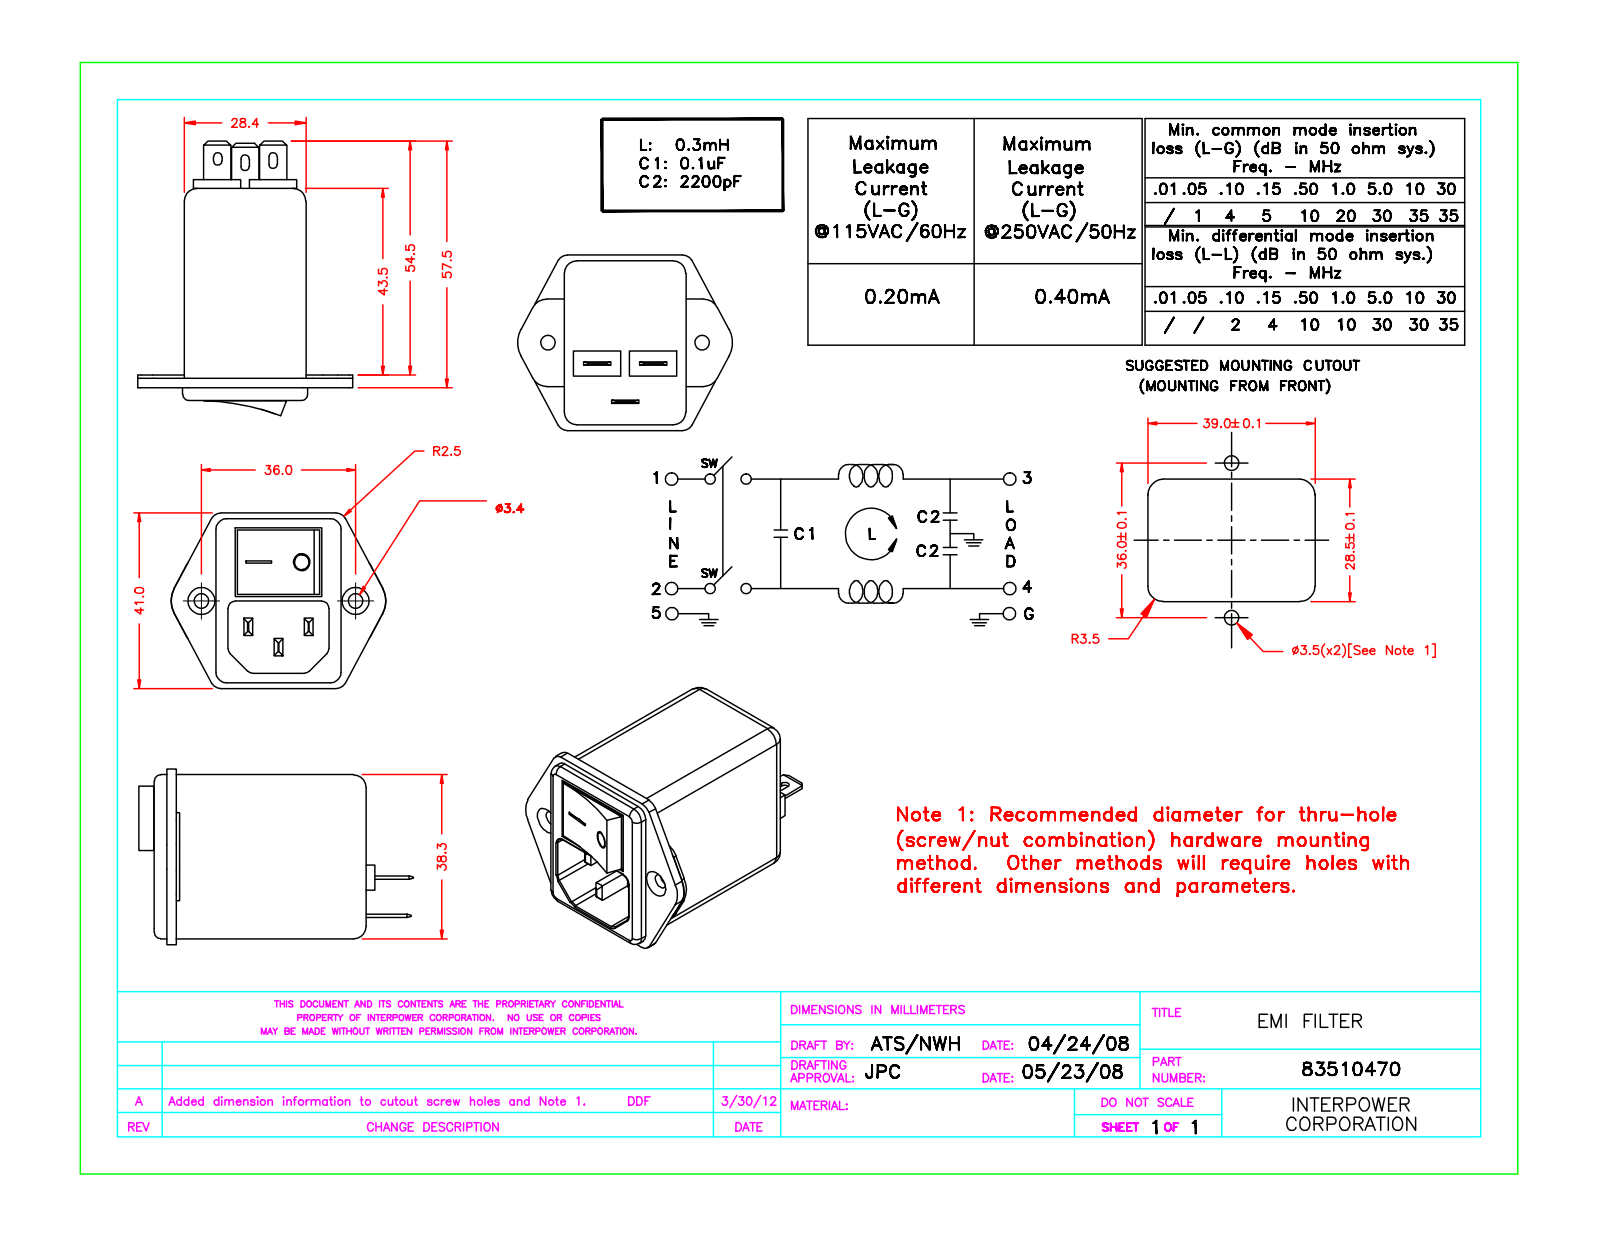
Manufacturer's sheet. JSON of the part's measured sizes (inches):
{"part_name": "10BEEG3G", "step_written_by": "SolidWorks 2008 (CONFIG_CONTROL_DESIGN)", "units": "inches", "bodies": {"solids": 2, "faces": 224, "planar": 132, "cylindrical": 67, "other": 25}, "overall_size": [2.52, 1.973, 1.614], "volume_in3": 3.03, "surface_area_in2": 19.28, "round_holes": [[0.134, 2], [0.157, 1]], "round_bosses_or_shafts": [[0.138, 1]], "partial_cylinders_radius": [[0.01, 12], [0.098, 8], [0.118, 8], [0.039, 6], [0.071, 6], [0.059, 4], [0.151, 4], [0.236, 2]], "face_to_face_distances": [1.118, 1.508, 0.754, 1.948, 1.831, 0.116, 0.089, 1.298, 0.534, 0.65], "hole_center_spacings": [1.417]}
